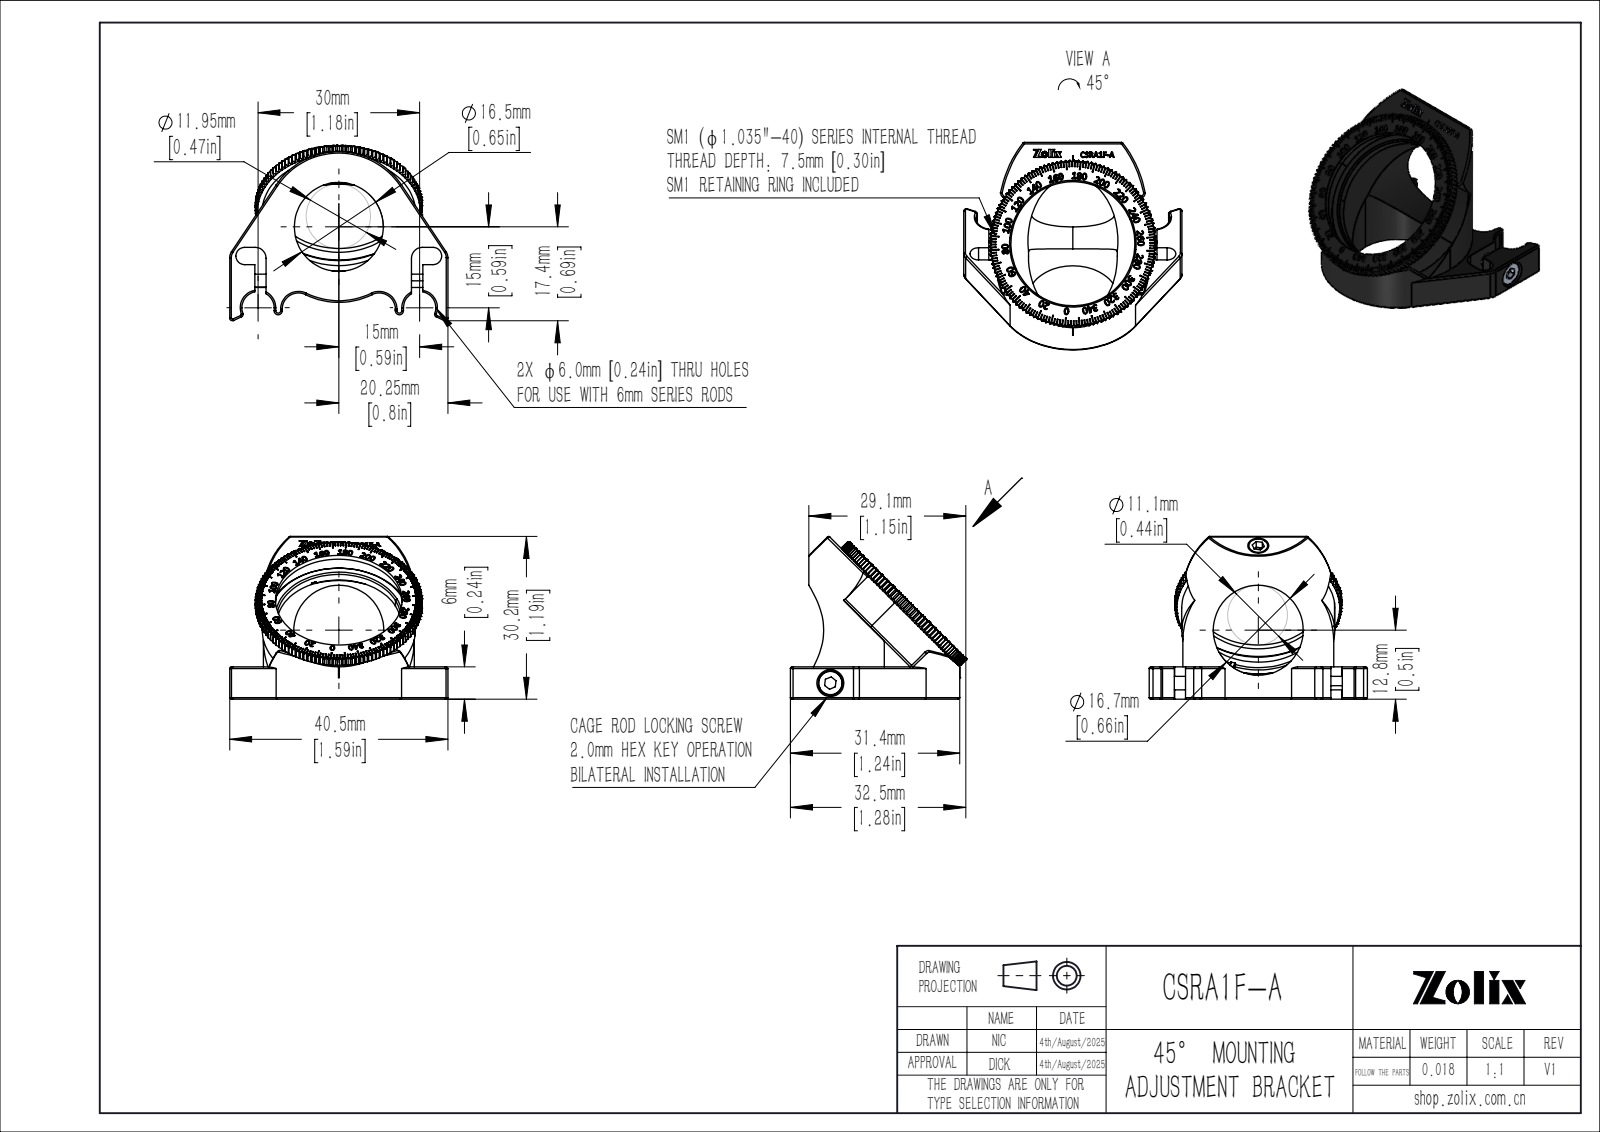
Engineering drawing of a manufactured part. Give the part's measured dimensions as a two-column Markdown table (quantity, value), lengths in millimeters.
| quantity | value |
| --- | --- |
| part name | CSRA1F-A |
| STEP written by | SolidWorks 2020 (CONFIG_CONTROL_DESIGN) |
| units | millimeters |
| bodies | 5 solids, 552 faces (300 planar, 95 cylindrical, 157 other) |
| overall size | 40.5 × 31.41 × 30.2 |
| volume | 5 639 mm³ |
| surface area | 5 076 mm² |
| round holes (diameter × count) | 2.05 × 1, 2.9 × 1, 3.3 × 1, 5 × 1, 16.5 × 1, 16.7 × 1, 23 × 1 |
| round bosses / shafts (diameter × count) | 2.5 × 2, 28 × 1, 26.29 × 1, 4.5 × 1, 4 × 1 |
| partial cylindrical surfaces (radius × count) | 0.3 × 21, 0.5 × 4, 2 × 4, 3 × 4, 0.75 × 2, 0.8 × 2, 1.25 × 2, 1.6 × 2 |
| main face-to-face distances | 6, 6.5, 2.55, 3.95, 1.9, 2.05, 4.6, 6.75, 33.75, 4.65 |
